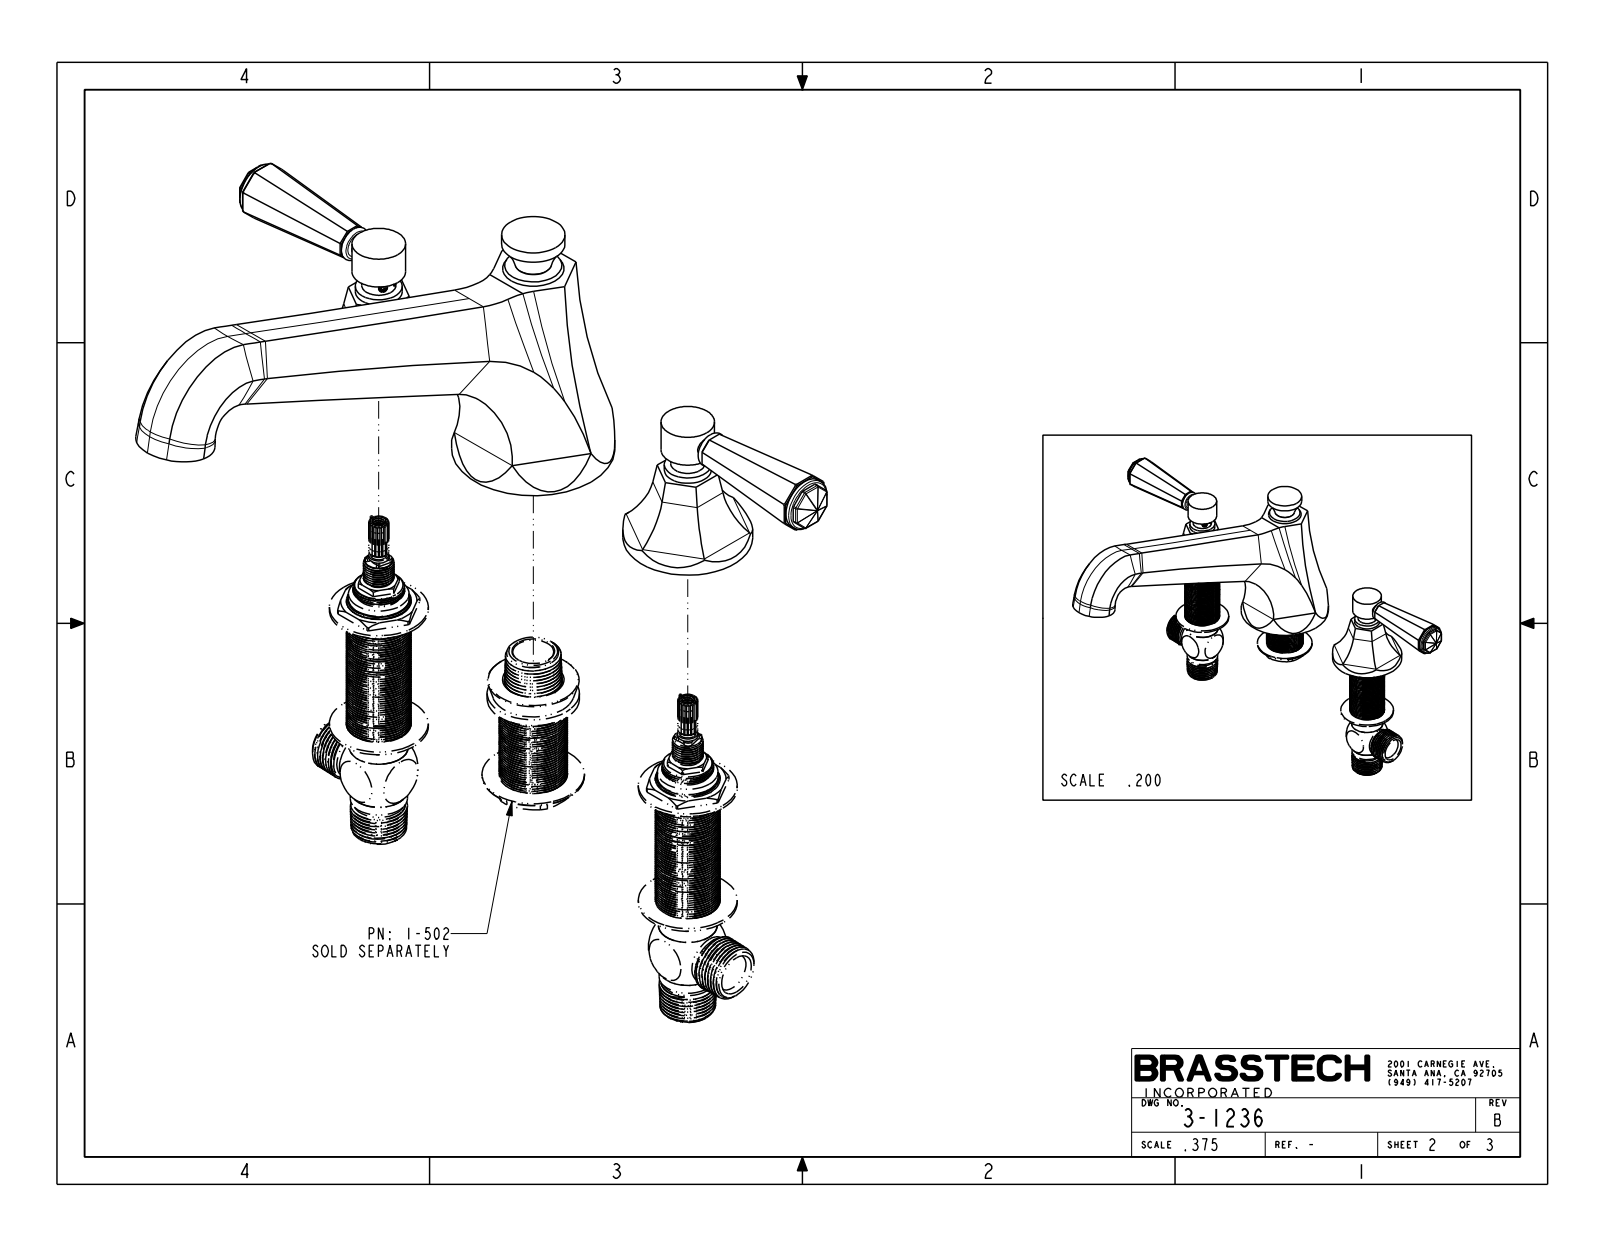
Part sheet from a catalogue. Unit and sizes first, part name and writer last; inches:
Units: inches
Overall size (bounding box): 14.716 × 11.484 × 6.573
Round holes (diameter × count): ⌀0.385 ×1
Round bosses / shafts (diameter × count): ⌀0.98 ×3, ⌀2.375 ×2, ⌀0.86 ×2, ⌀0.625 ×2, ⌀0.4 ×2, ⌀2.99 ×1, ⌀1.16 ×1, ⌀0.365 ×1
Partial cylindrical surfaces — rounded edges, fillets, slot ends (radius × count): R0.03 ×40, R1.541 ×12, R13 ×6, R2.75 ×1
Main face-to-face distances: 0.169, 0.168, 3.928, 1.647, 1.977, 0.33, 4.115, 2.468, 2.138, 4.045
Volume: 44.47 in³ · Surface area: 141.9 in²
Bodies: 4 solids, 361 faces (145 planar, 105 cylindrical, 111 other)
Part name (STEP PRODUCT): 3-1236
STEP written by: CREO PARAMETRIC BY PTC INC, 2018400 (CONFIG_CONTROL_DESIGN)
